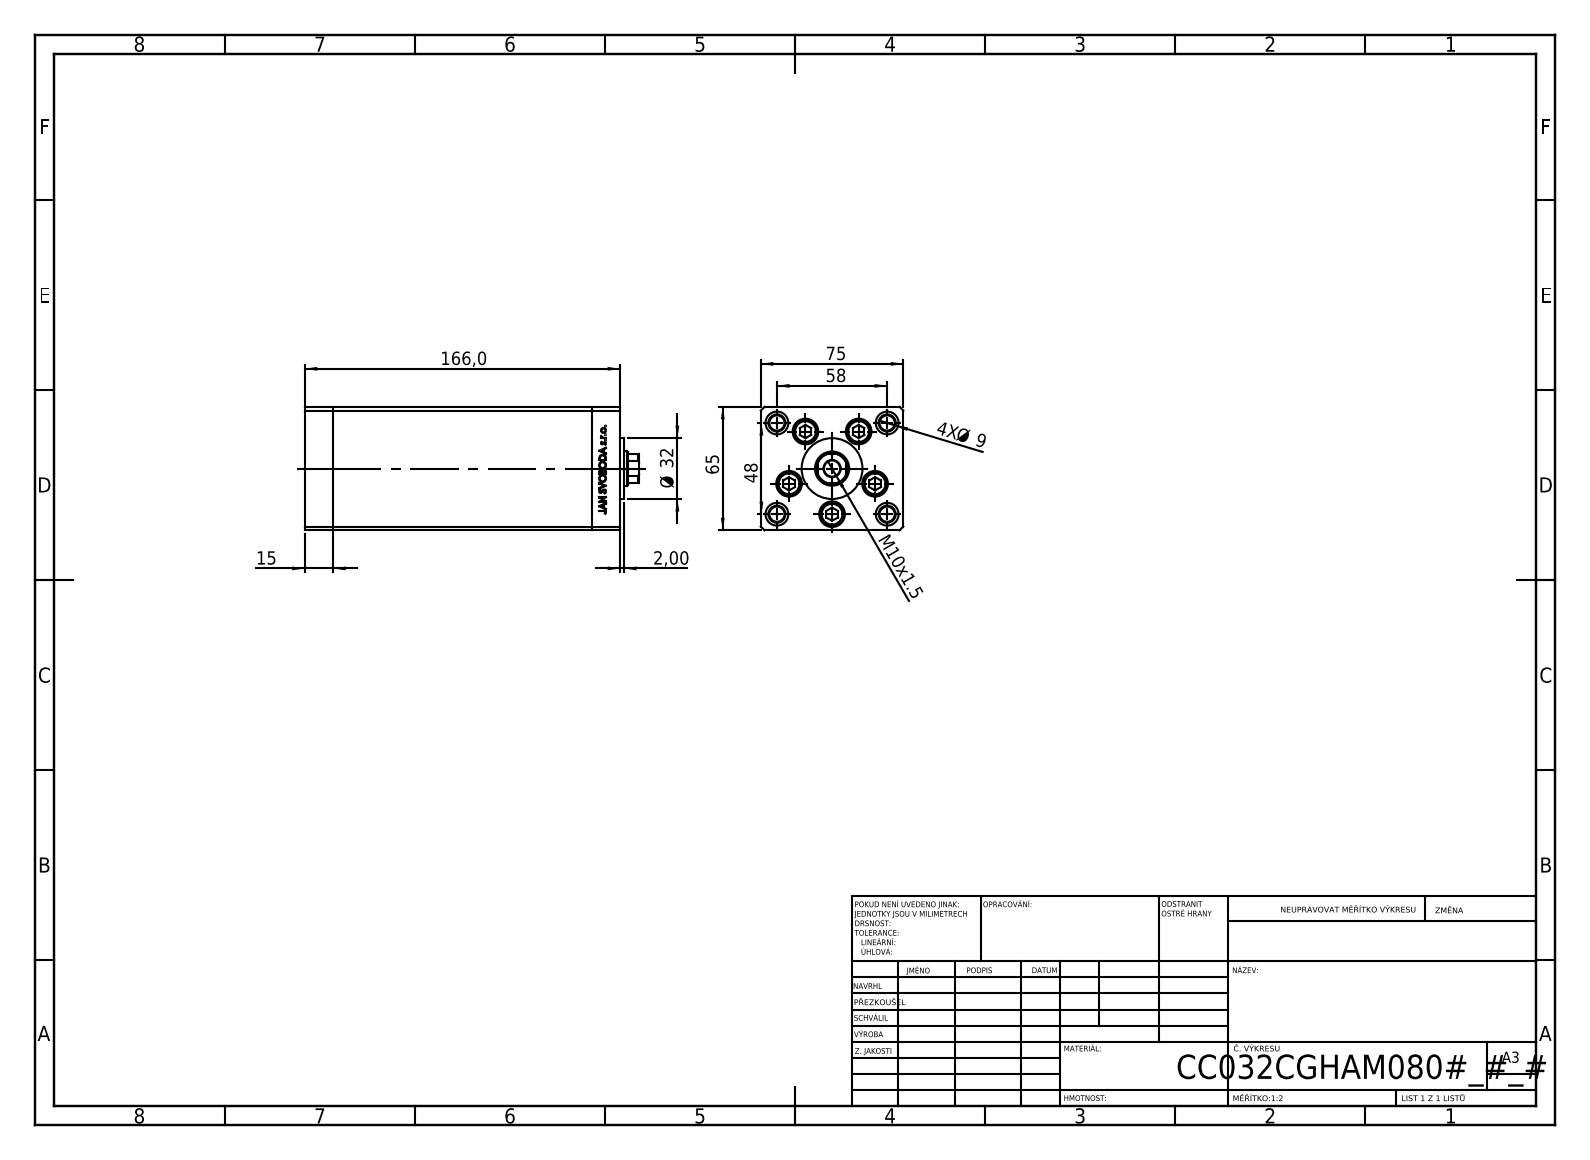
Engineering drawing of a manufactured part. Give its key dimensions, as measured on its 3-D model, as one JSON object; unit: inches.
{"part_name": "V220C_C MIDDLE; V220C BACK_C; V220C FRONT; V220C_VC_C (+1 more)", "step_written_by": "SolidWorks 2019 (CONFIG_CONTROL_DESIGN)", "units": "inches", "bodies": {"solids": 13, "faces": 1179, "planar": 542, "cylindrical": 175, "other": 462}, "overall_size": [6.929, 2.953, 2.559], "volume_in3": 41.31, "surface_area_in2": 222.8, "round_holes": [[0.354, 9], [0.531, 5], [0.079, 4], [0.315, 4], [0.472, 4], [0.518, 4], [0.335, 1], [0.492, 1], [0.709, 1]], "round_bosses_or_shafts": [[0.315, 5], [0.492, 4], [1.26, 1]], "partial_cylinders_radius": [[0.037, 2], [0.335, 1]], "face_to_face_distances": [2.953, 2.559, 0.591, 5.354, 5.945, 6.535, 1.102, 0.512, 5.591, 0.354], "hole_center_spacings": [0.945, 1.482, 0.617, 0.678, 1.091, 1.135, 1.142, 1.285]}
